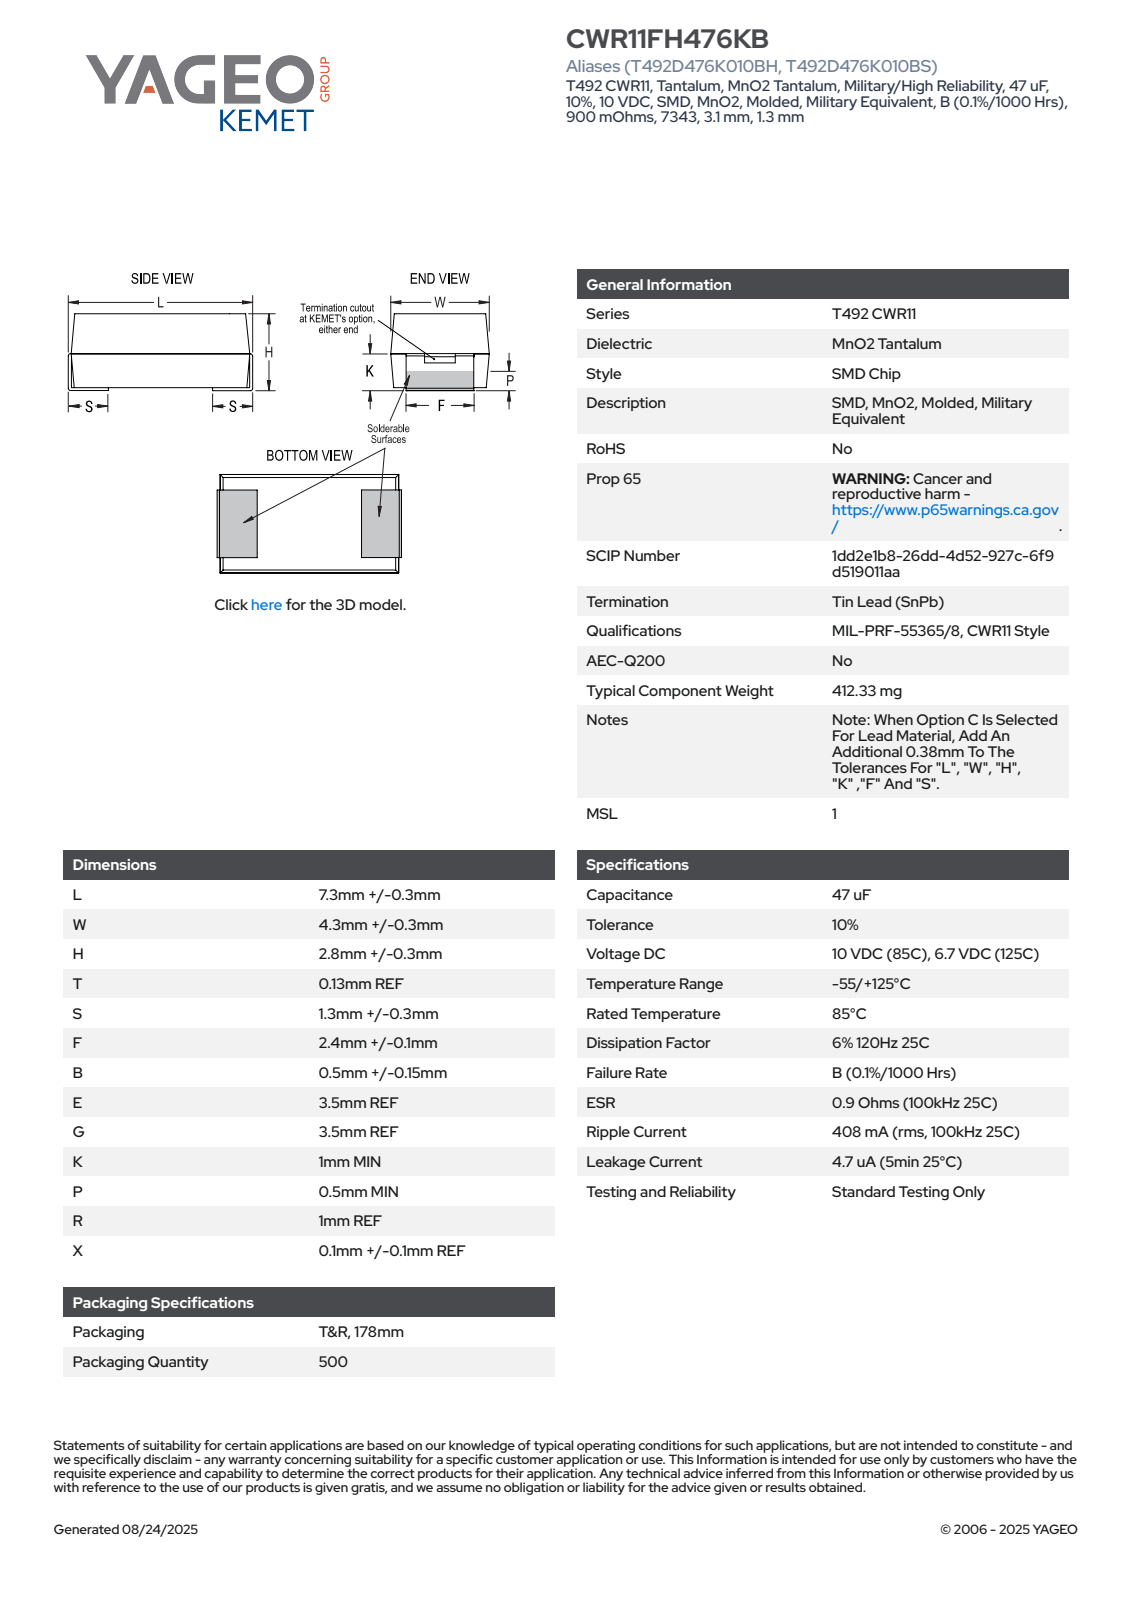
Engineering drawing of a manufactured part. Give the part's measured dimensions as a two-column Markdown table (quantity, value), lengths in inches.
| quantity | value |
| --- | --- |
| part name | CTS_TCM3M_7343_L7.6H3.1S1.3F2.5K1P0.5W4.6 |
| STEP written by | SolidWorks 2014 (AUTOMOTIVE_DESIGN) |
| units | inches |
| bodies | 4 solids, 85 faces (81 planar, 4 cylindrical, 0 other) |
| overall size | 0.299 × 0.181 × 0.126 |
| volume | 0.006 in³ |
| surface area | 0.225 in² |
| partial cylindrical surfaces (radius × count) | 0.004 × 4 |
| main face-to-face distances | 0.122, 0.126, 0.295, 0.291, 0.299, 0.051, 0.047, 0.248, 0.244, 0.098 |
